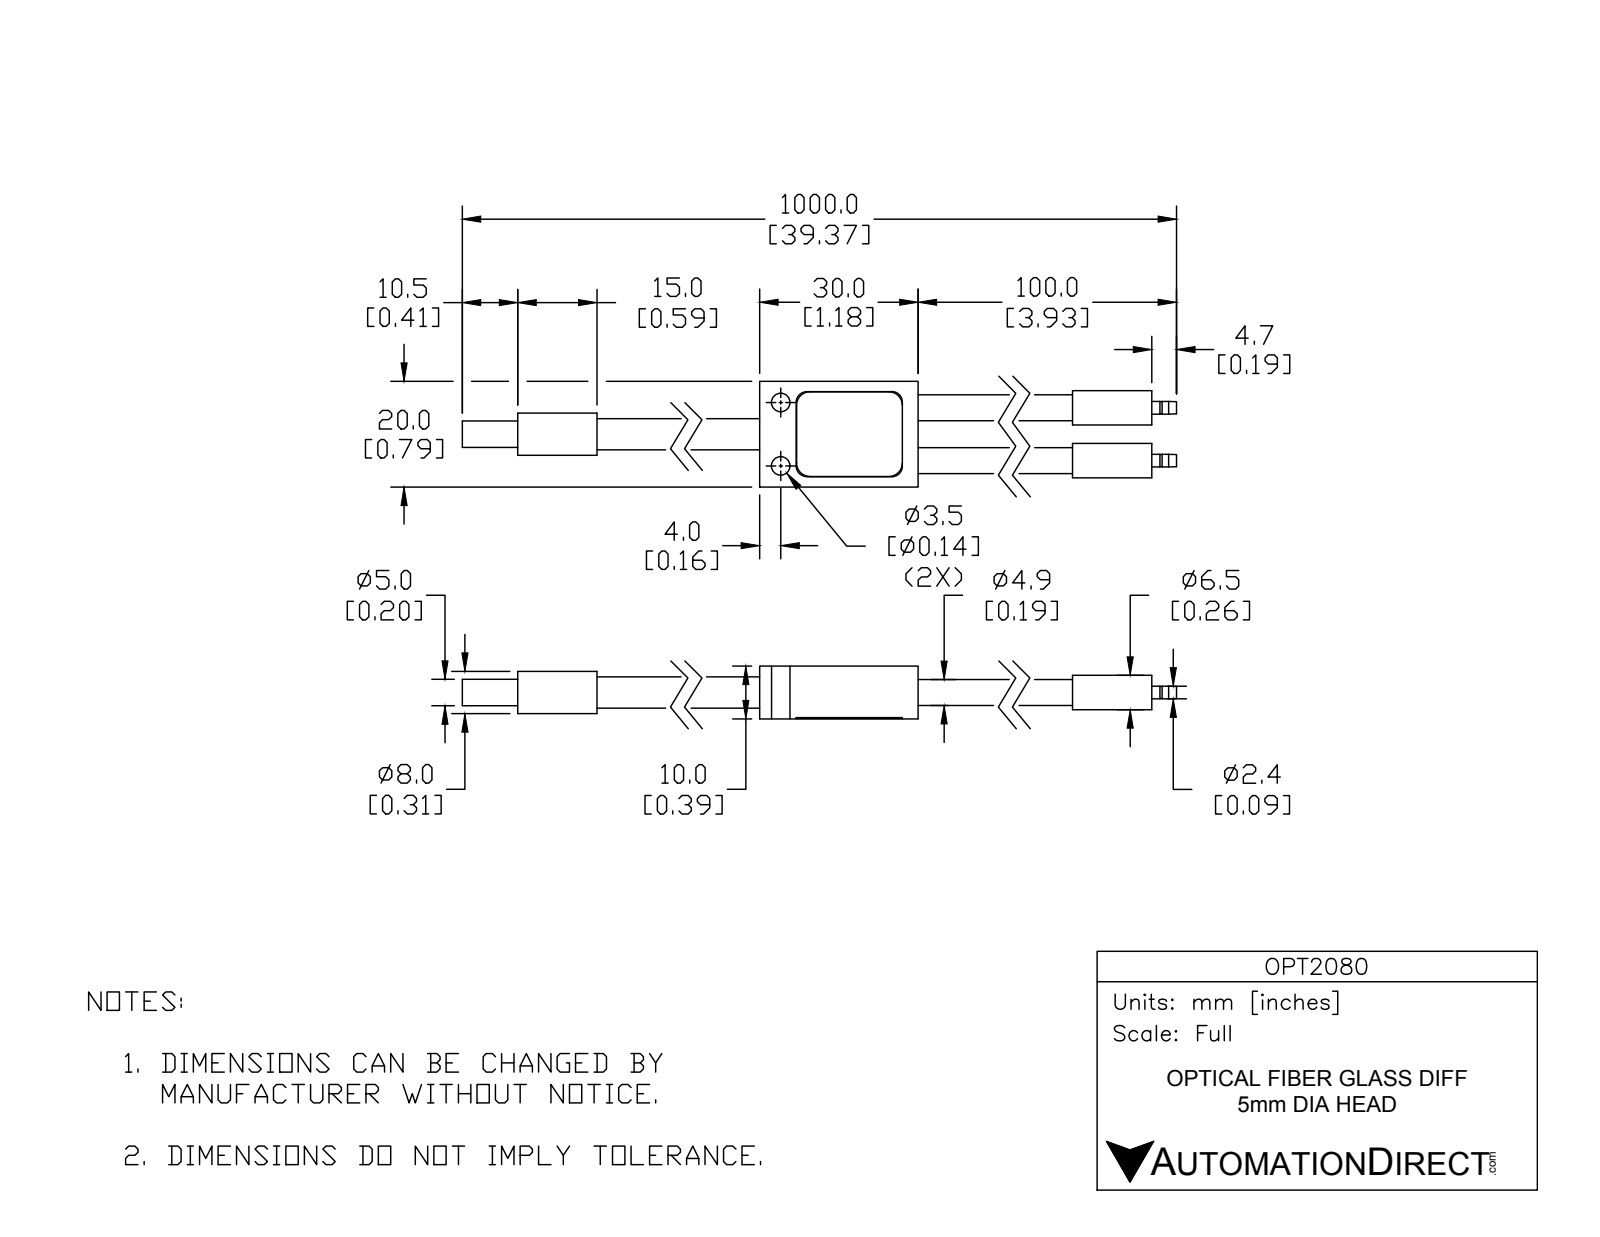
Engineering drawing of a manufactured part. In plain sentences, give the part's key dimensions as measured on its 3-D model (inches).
The part is named "OPT2080". Its 3-D file was written by "SolidWorks 2014 (AUTOMOTIVE_DESIGN)". It is 1 solid with 70 faces: 24 planar, 34 cylindrical and 12 other. Overall it measures 39.37 by 0.787 by 0.394 inches. Its volume is 2.068 cubic inches and its surface area 33.88 square inches. Round holes: 2 of diameter 0.138. Round bosses or shafts: 2 of diameter 0.256, 2 of diameter 0.193, 2 of diameter 0.094, 1 of diameter 0.315, 1 of diameter 0.232, 1 of diameter 0.197. Partial cylindrical surfaces (rounded edges, fillets, slot ends): 4 of radius 0.098, 2 of radius 0.079, 2 of radius 0.083. The main face-to-face distances are 0.39, 0.787, 0.394, 1.181, 4.933, 3.752, 0.591, 38.181, 33.839, 35.02. The hole center spacings are 0.472.
